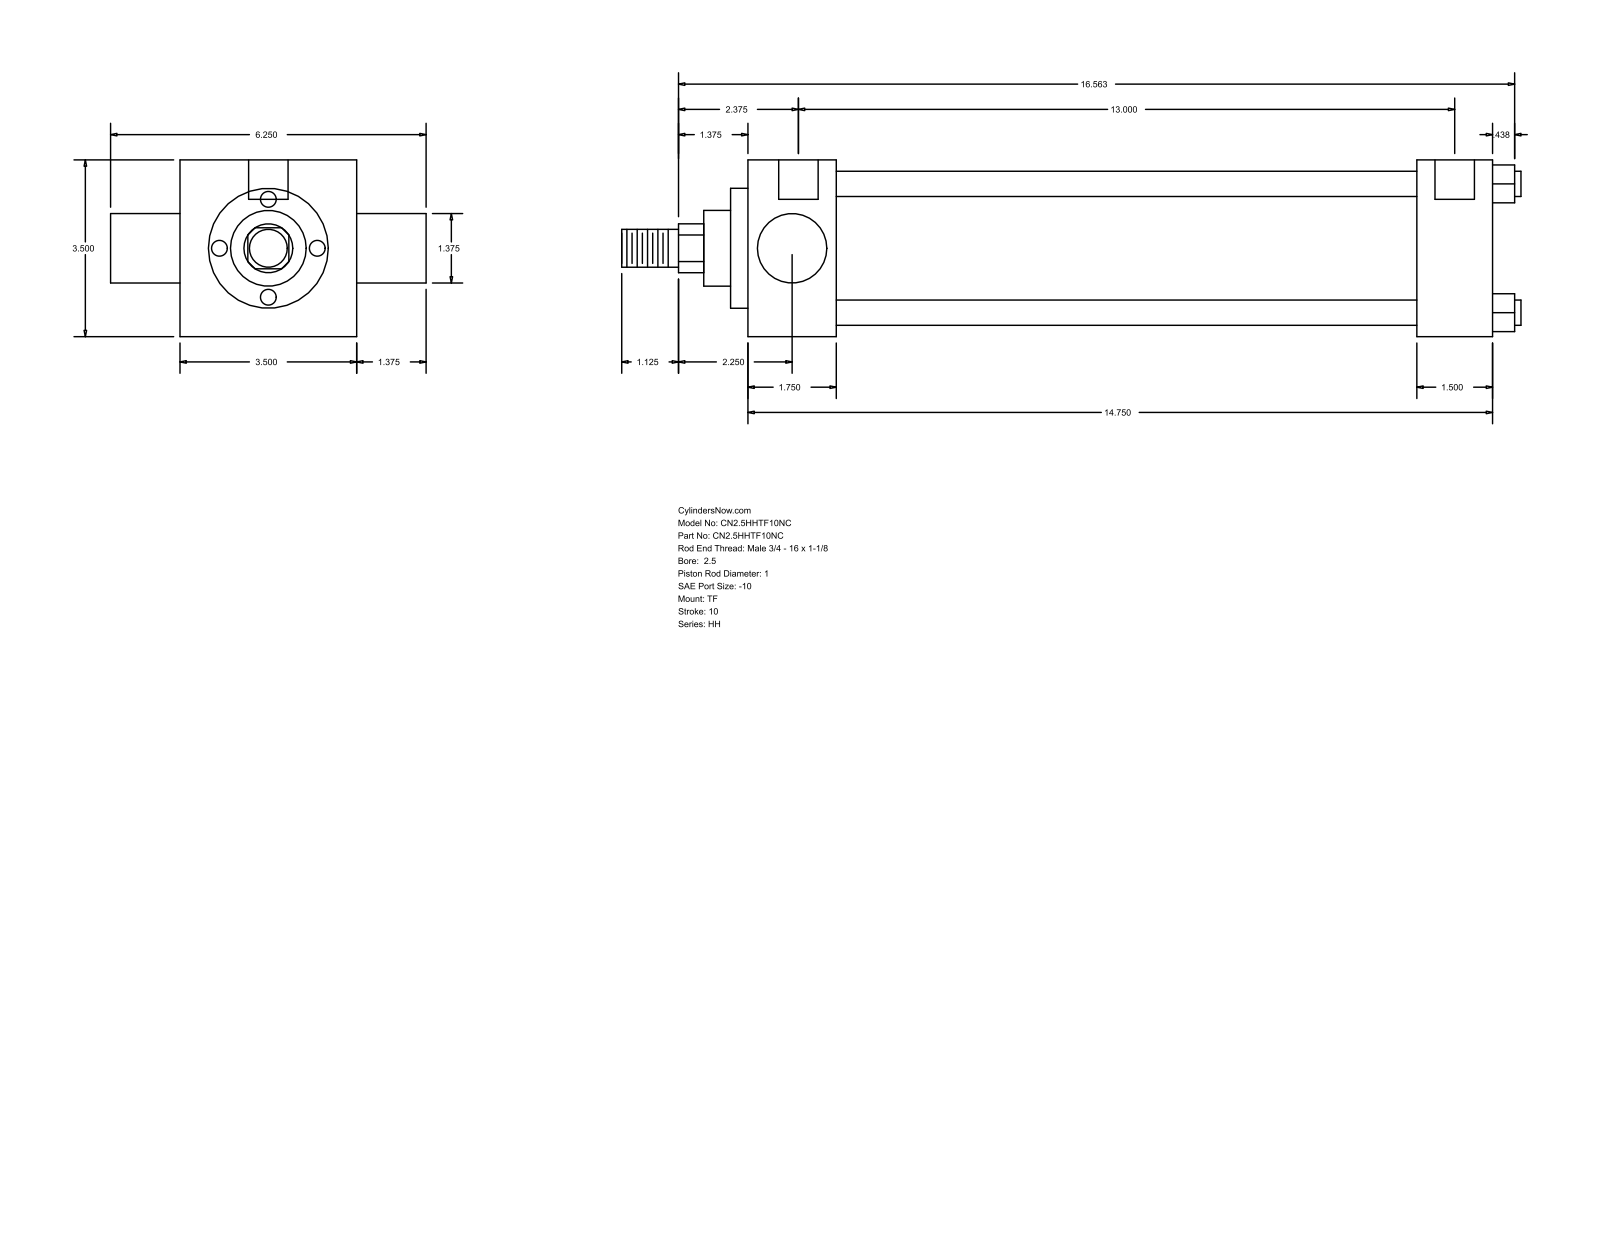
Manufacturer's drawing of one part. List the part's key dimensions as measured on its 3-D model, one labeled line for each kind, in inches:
Part name (STEP PRODUCT): HH_TF__0250_1
STEP written by: GSSL Pune (CONFIG_CONTROL_DESIGN)
Units: inches
Bodies: 0 solids, 86 faces (61 planar, 25 cylindrical, 0 other)
Overall size (bounding box): 17.813 × 6.25 × 3.5
Round holes (diameter × count): ⌀0.219 ×3, ⌀0.781 ×2
Round bosses / shafts (diameter × count): ⌀0.5 ×4, ⌀2.875 ×1, ⌀2.375 ×1, ⌀1.5 ×1, ⌀1.375 ×1, ⌀1 ×1, ⌀0.75 ×1
Partial cylindrical surfaces — rounded edges, fillets, slot ends (radius × count): R0.484 ×1
Main face-to-face distances: 3.5, 14.75, 1.75, 13, 13.25, 11.5, 1.5, 1.375, 4.875, 0.344
Hole centre spacings: 0.063, 13.062, 13, 13.125
